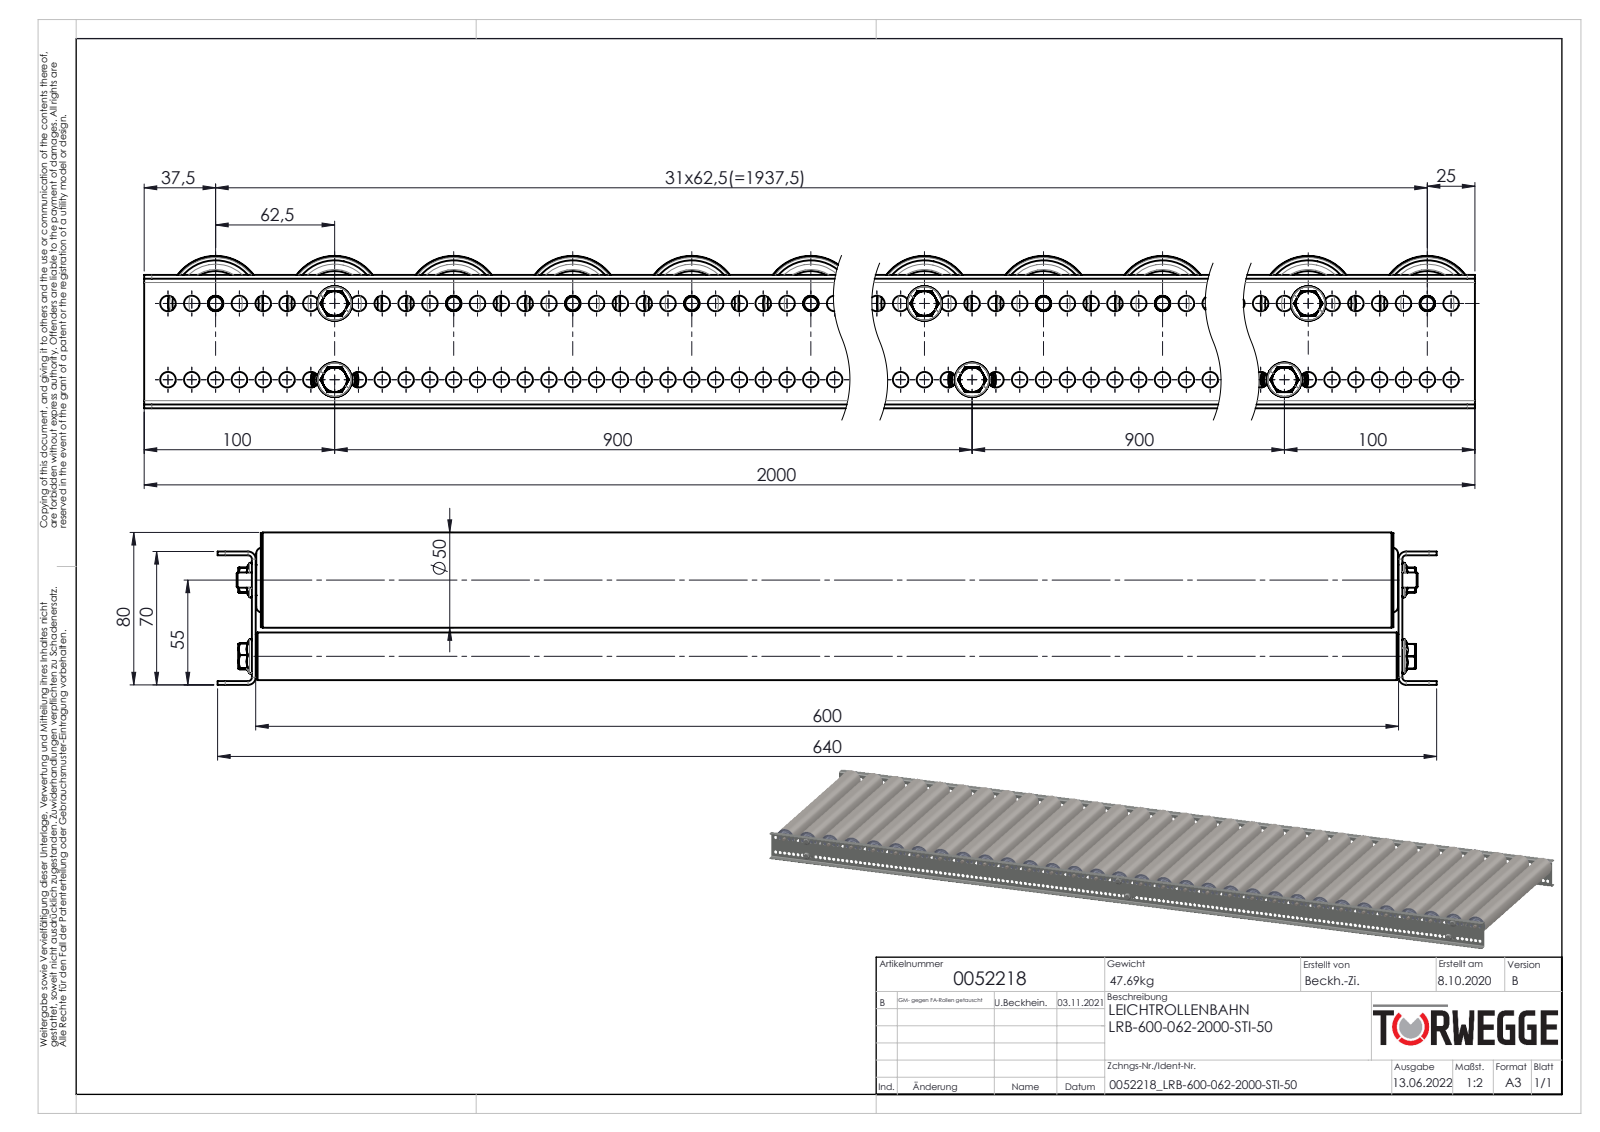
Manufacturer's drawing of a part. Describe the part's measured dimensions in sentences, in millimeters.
The part is named "S100994_Sperrzahnschraube_M08x16-8.8-A2K; Druckfeder_1,2x10x30; 0052218; TRG-50x1,5-STI-A8-FA_KFG_0050888_TRG-50x1,5-STI-A8-FA-EL=600 (+8 more)". Its 3-D file was written by "SolidWorks 2020 (AUTOMOTIVE_DESIGN)". It is 728 solids with 12550 faces: 2508 planar, 4480 cylindrical and 5562 other. Overall it measures 2000 by 640 by 80 millimeters. Its volume is 7 066 000 cubic millimeters and its surface area 8 316 000 square millimeters. Round holes: 318 of diameter 8.2, 32 of diameter 17.1, 32 of diameter 18.5, 32 of diameter 27.7, 32 of diameter 45.3, 32 of diameter 47, 29 of diameter 7.6, 6 of diameter 6.8, 3 of diameter 12, 3 of diameter 12.2, 3 of diameter 19.2, 3 of diameter 21. Round bosses or shafts: 35 of diameter 8, 32 of diameter 50, 32 of diameter 49.5, 32 of diameter 47.3, 32 of diameter 29.7, 32 of diameter 27.4, 32 of diameter 27.3, 32 of diameter 16. Partial cylindrical surfaces (rounded edges, fillets, slot ends): 58 of radius 0.6, 58 of radius 0.75, 58 of radius 2.45, 29 of radius 4.87, 29 of radius 7, 12 of radius 2.5, 8 of radius 4, 4 of radius 2. The main face-to-face distances are 2, 602, 68, 600, 604, 70, 66, 1, 2.3, 601.7. The hole center spacings are 12.5, 25, 37.5, 50, 62.5, 75, 87.5, 100.
